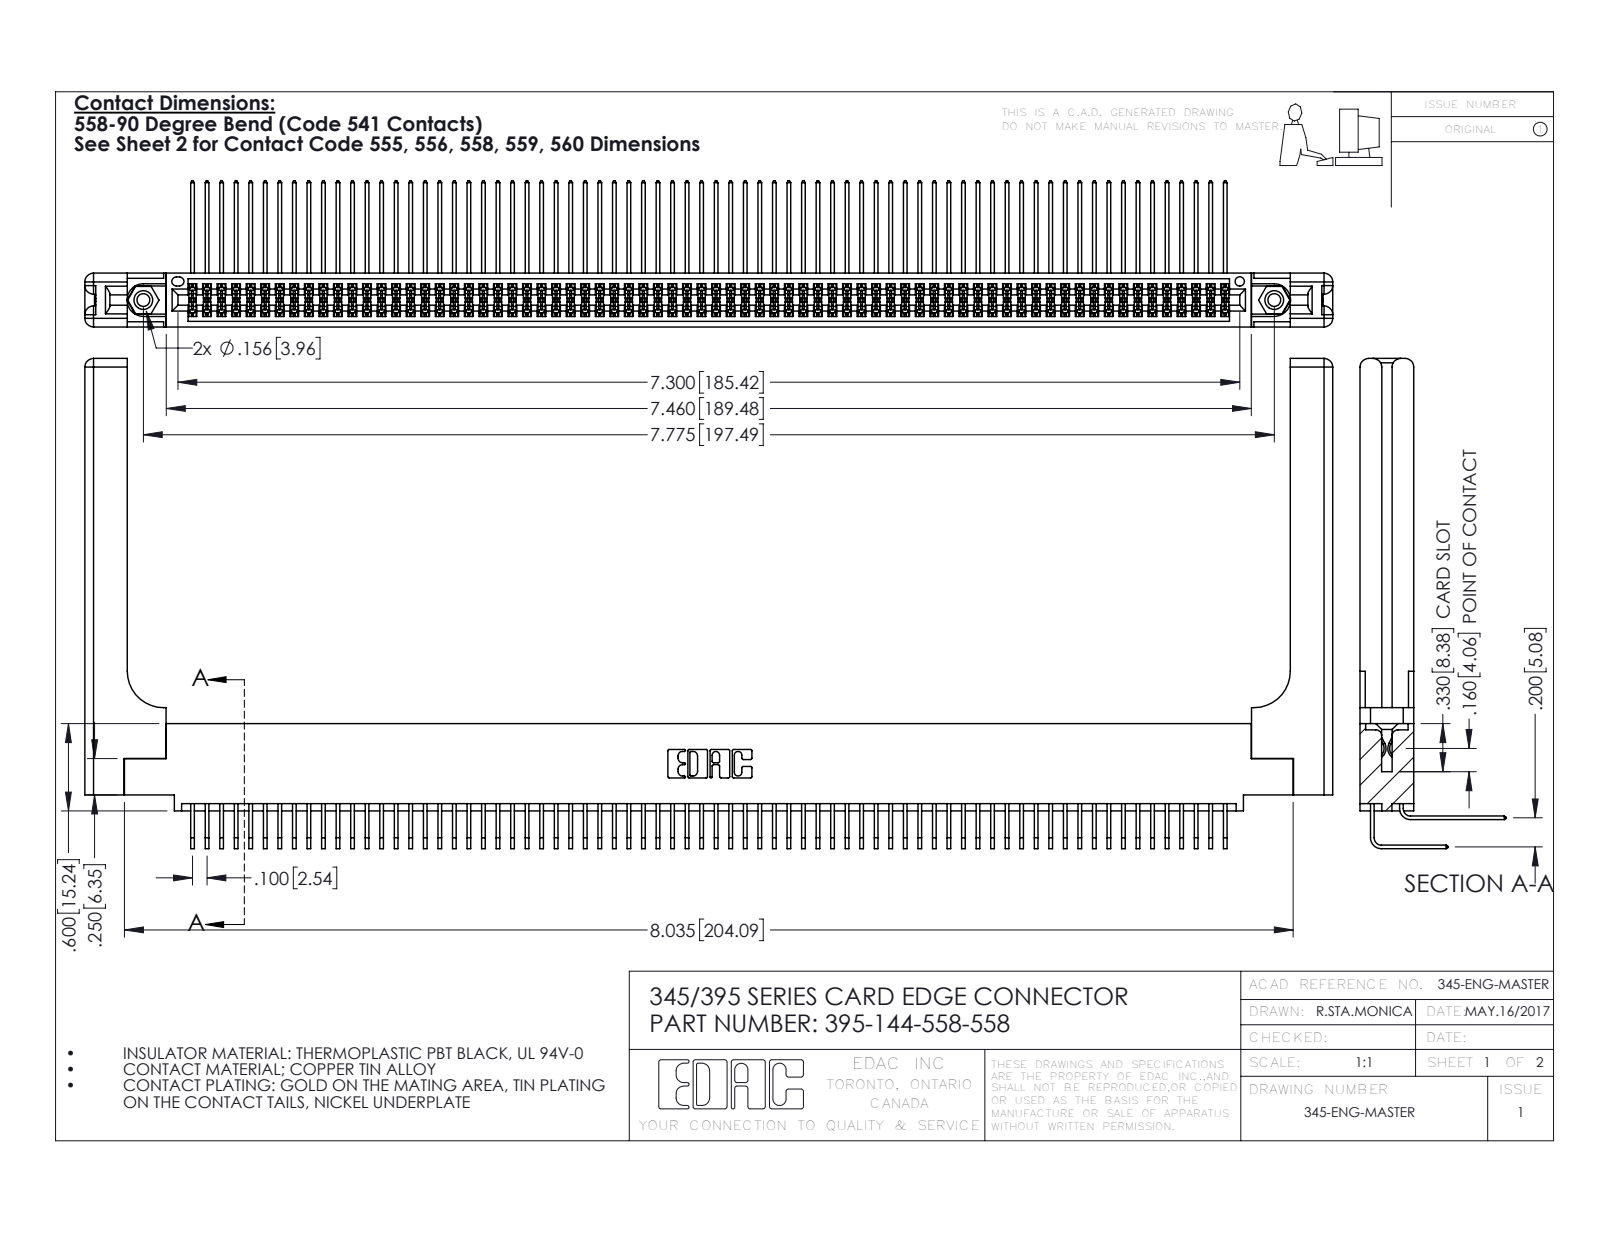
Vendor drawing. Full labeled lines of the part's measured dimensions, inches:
Part name (STEP PRODUCT): 345-220-058_345-220-058; 345-292-001_558 Tail - 2; 345-292-001_558 559 Tail - 1; 395-144-558-558 (+2 more)
STEP written by: SolidWorks 2016 (CONFIG_CONTROL_DESIGN)
Units: inches
Bodies: 149 solids, 7874 faces (5272 planar, 2542 cylindrical, 60 other)
Overall size (bounding box): 8.579 × 3.369 × 1.005
Volume: 1.872 in³ · Surface area: 65.81 in²
Round holes (diameter × count): ⌀0.089 ×2, ⌀0.125 ×2, ⌀0.156 ×2, ⌀0.064 ×1
Round bosses / shafts (diameter × count): ⌀0.155 ×2
Partial cylindrical surfaces — rounded edges, fillets, slot ends (radius × count): R0.006 ×216, R0.01 ×22, R0.06 ×16, R0.007 ×6, R0.031 ×6, R0.026 ×3, R0.014 ×2, R0.019 ×2
Main face-to-face distances: 0.072, 0.298, 0.37, 0.2, 0.098, 0.272, 0.025, 0.225, 0.025, 0.175
Hole centre spacings: 0.27, 7.539, 7.775
